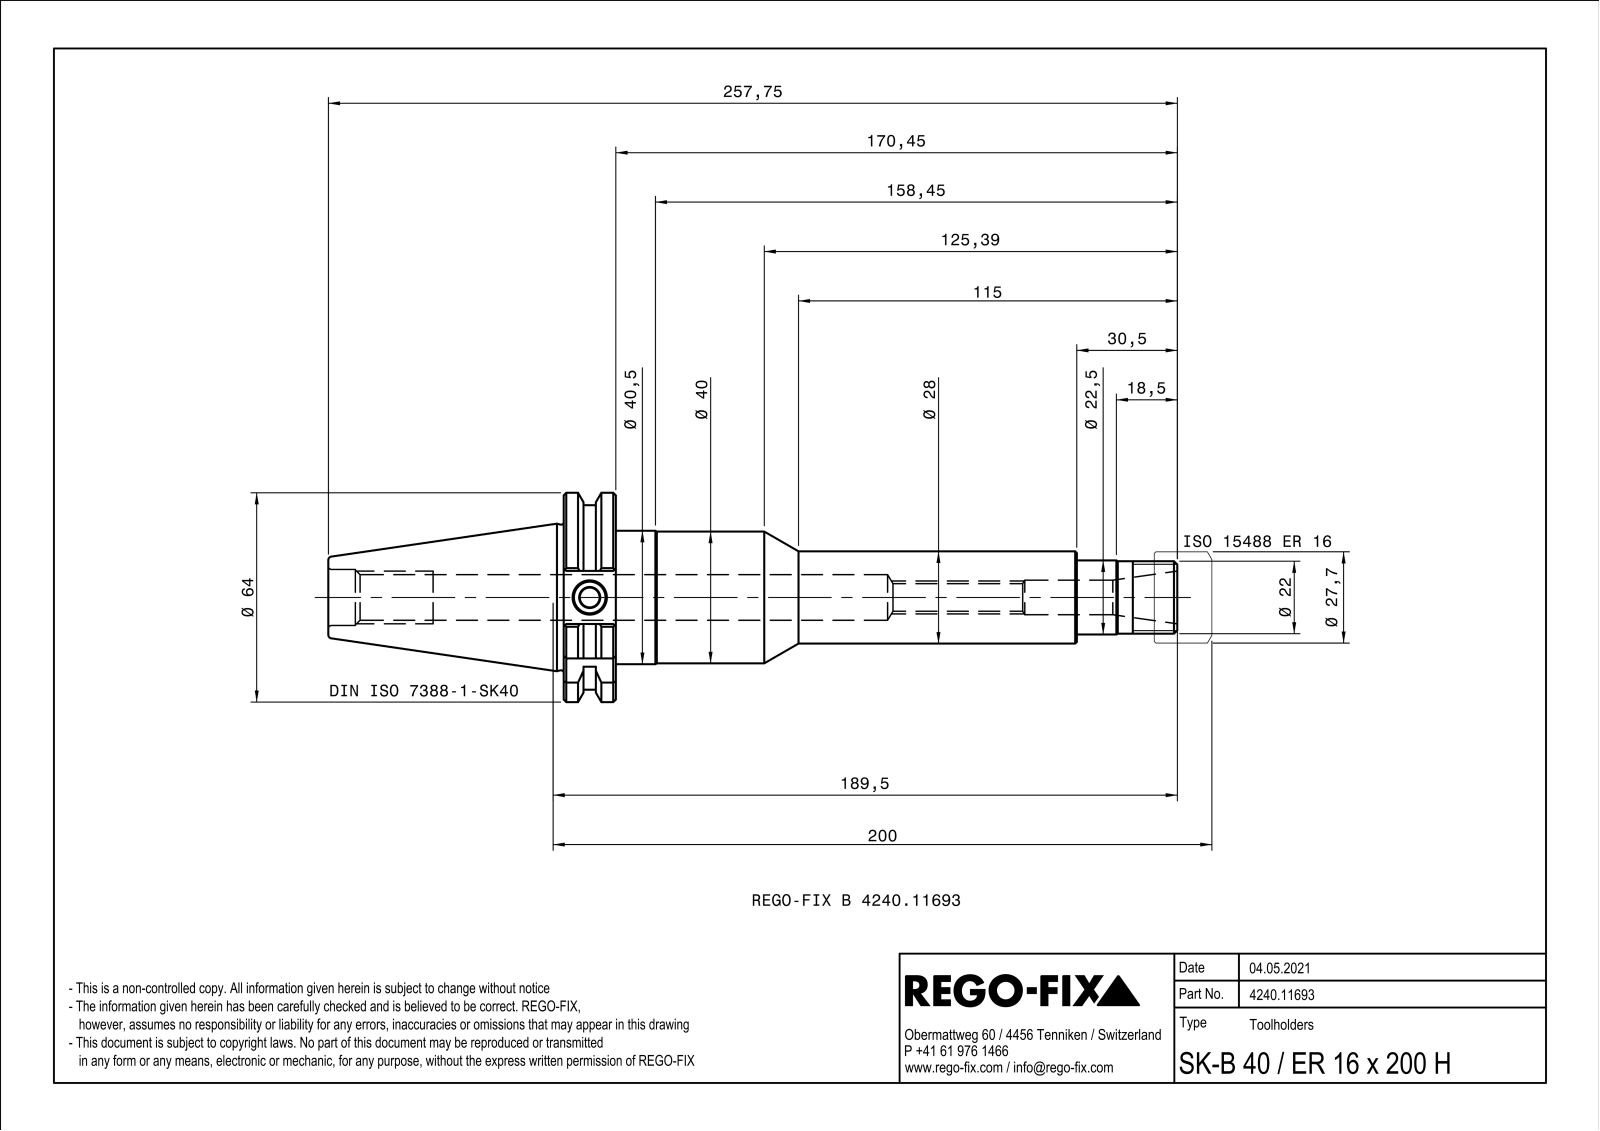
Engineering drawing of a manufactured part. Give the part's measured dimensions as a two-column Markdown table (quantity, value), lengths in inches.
| quantity | value |
| --- | --- |
| part name | NOCUT |
| STEP written by | SIEMENS PLM Software Solid Edge ST10 (AUTOMOTIVE_DESIGN) |
| units | inches |
| bodies | 2 solids, 311 faces (85 planar, 101 cylindrical, 125 other) |
| overall size | 10.163 × 2.514 × 2.411 |
| volume | 25.75 in³ |
| surface area | 134.3 in² |
| round holes (diameter × count) | 0.138 × 5, 0.154 × 2, 0.128 × 1, 0.236 × 1, 0.33 × 1, 0.394 × 1, 0.413 × 1, 0.544 × 1, 0.545 × 1, 0.657 × 1, 0.669 × 1 |
| round bosses / shafts (diameter × count) | 1.606 × 1, 1.594 × 1, 1.587 × 1, 1.575 × 1, 1.114 × 1, 1.102 × 1, 0.898 × 1, 0.886 × 1 |
| partial cylindrical surfaces (radius × count) | 0.02 × 13, 0.089 × 2, 1.102 × 1, 1.251 × 1, 1.257 × 1 |
| main face-to-face distances | 0.624, 1.862, 0.634, 10.156, 0.387, 0.237, 0.239, 0.148, 0.385, 0.411 |
